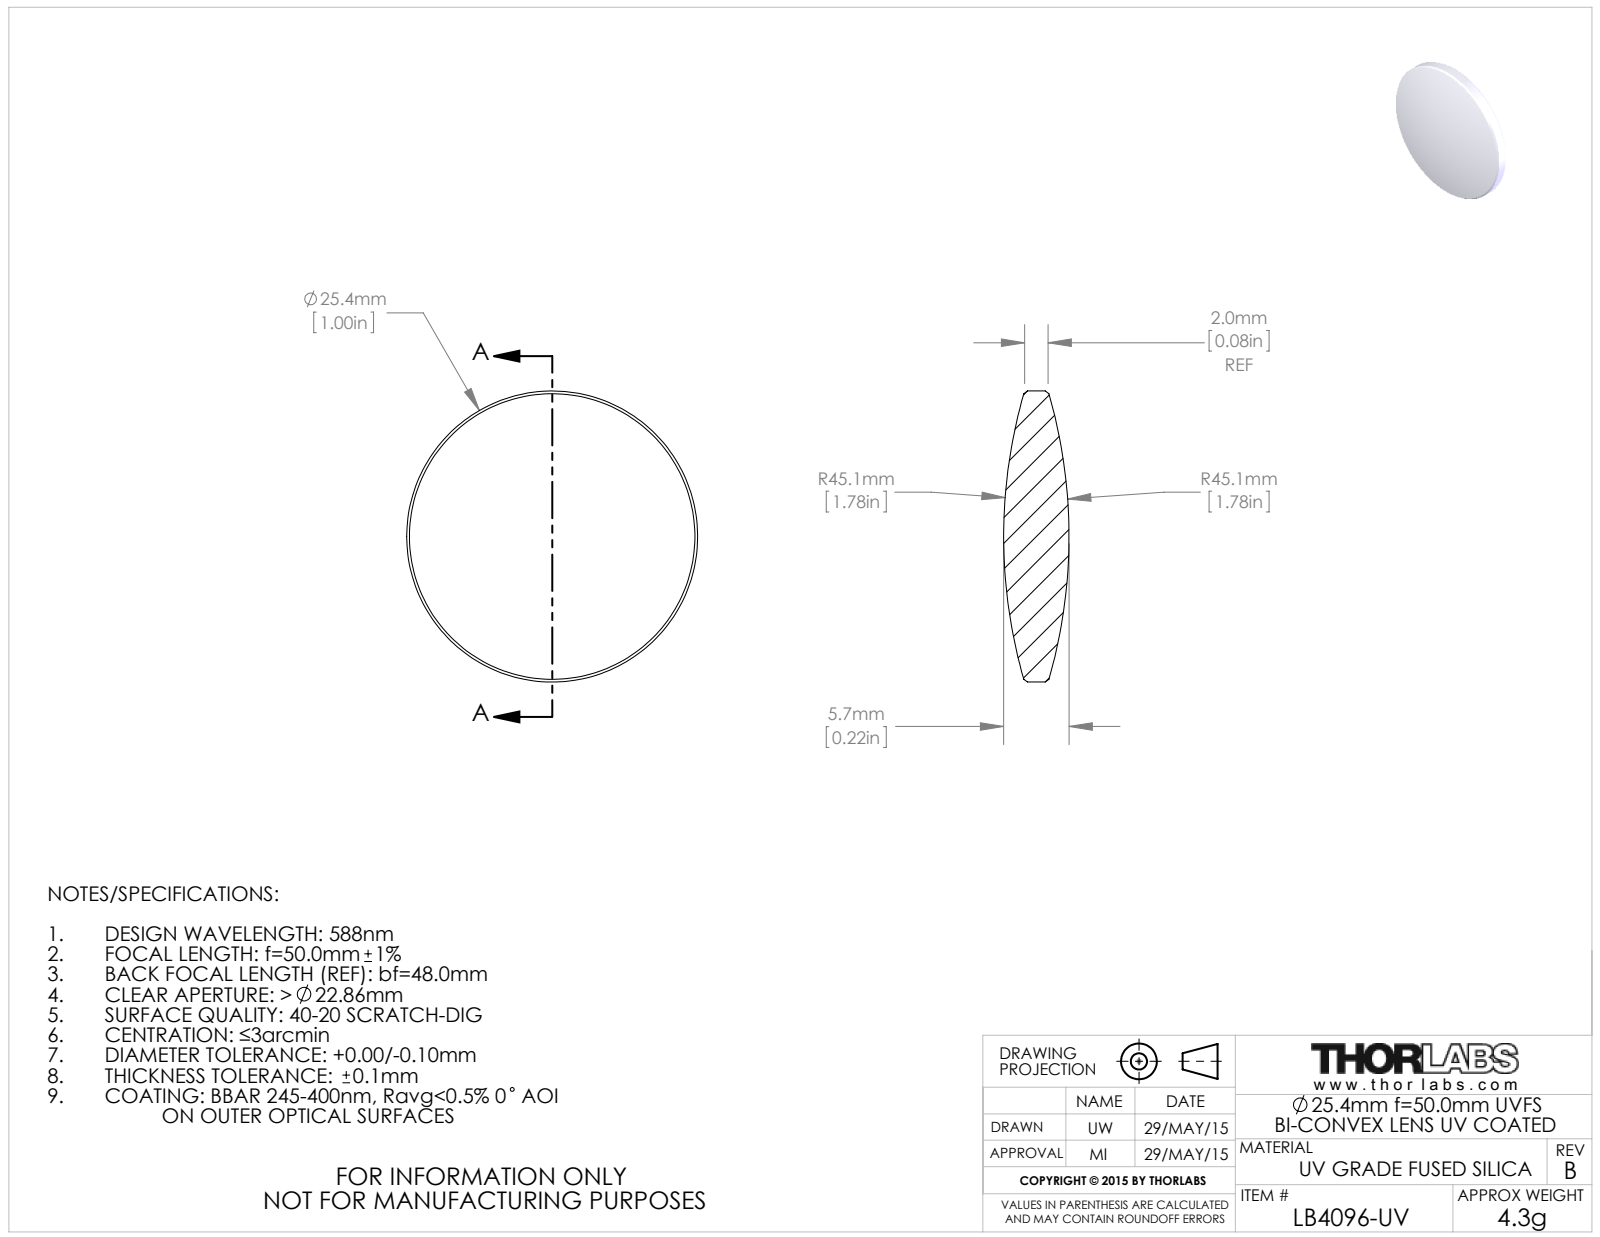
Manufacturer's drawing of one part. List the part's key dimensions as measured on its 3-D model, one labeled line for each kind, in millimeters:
Part name (STEP PRODUCT): 4319-E0W
STEP written by: SolidWorks 2014 (CONFIG_CONTROL_DESIGN)
Units: millimetres
Bodies: 1 solid, 10 faces (0 planar, 2 cylindrical, 8 other)
Overall size (bounding box): 25.4 × 25.4 × 5.7
Volume: 1 965 mm³ · Surface area: 1 182 mm²
Round bosses / shafts (diameter × count): ⌀25.4 ×1
